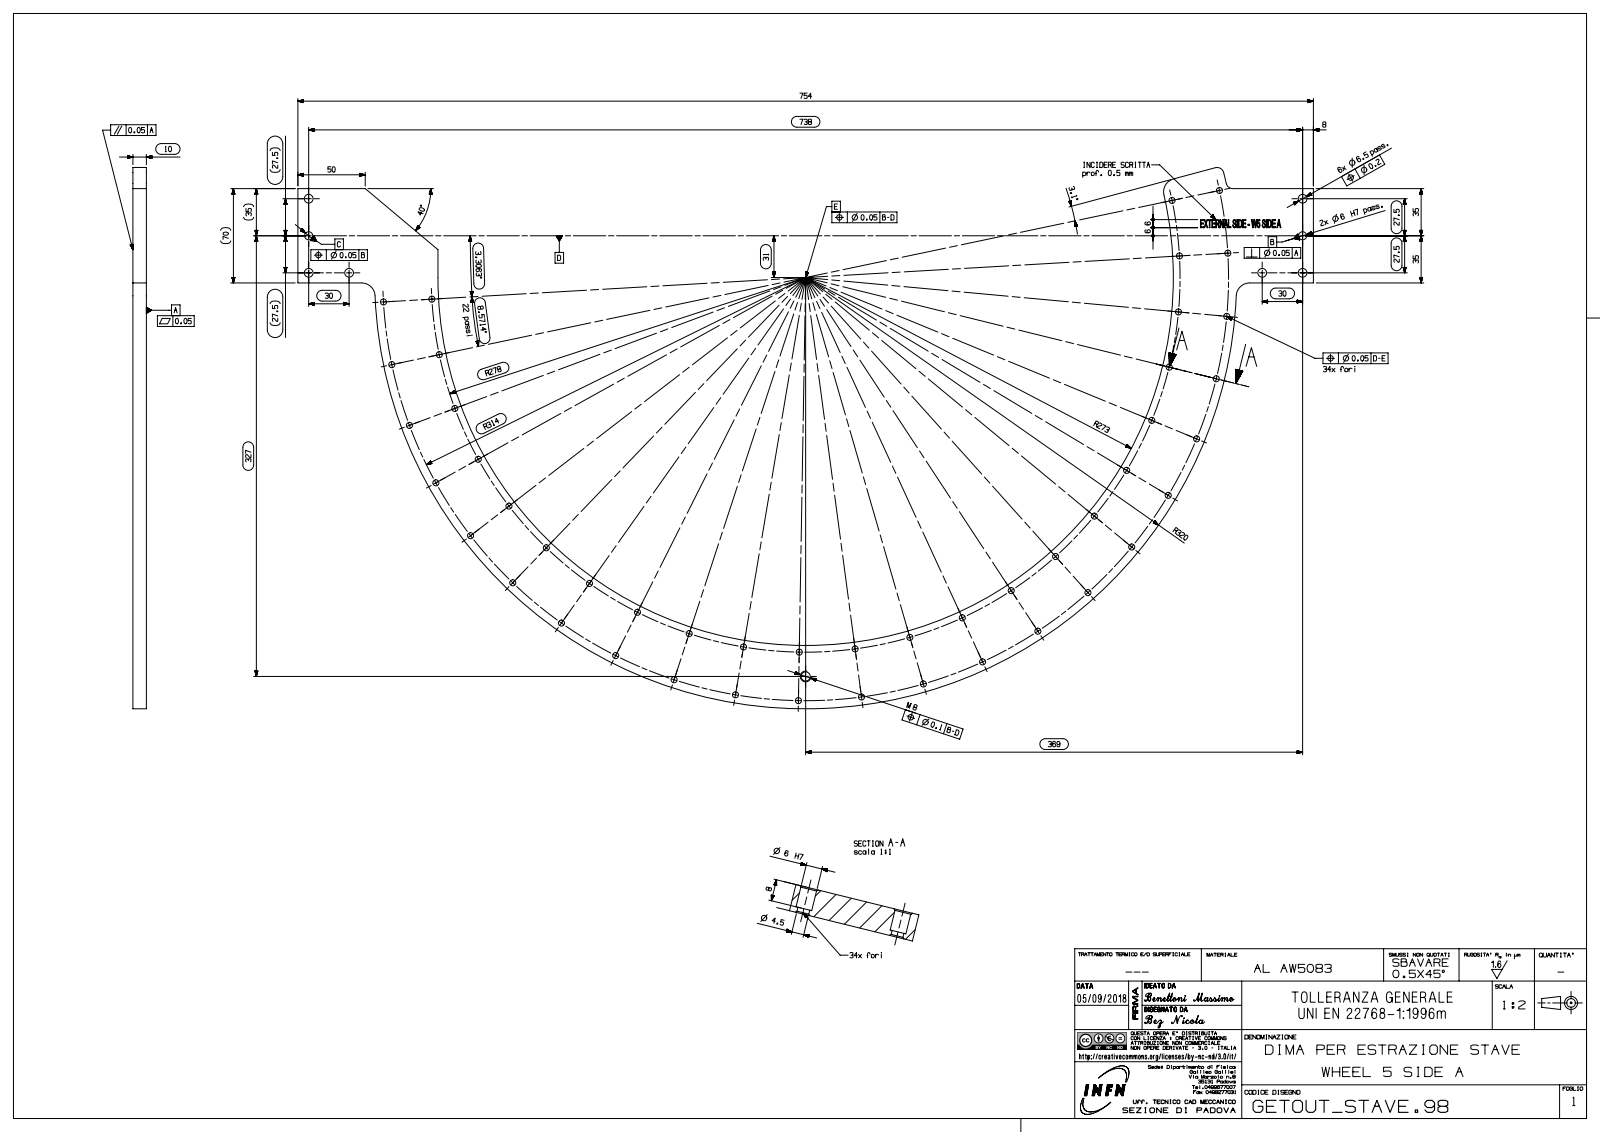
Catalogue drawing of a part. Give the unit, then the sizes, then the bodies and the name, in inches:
Units: inches
Overall size (bounding box): 29.685 × 15.815 × 0.394
Round holes (diameter × count): ⌀0.236 ×48, ⌀0.177 ×46, ⌀0.256 ×6, ⌀0.268 ×1
Partial cylindrical surfaces — rounded edges, fillets, slot ends (radius × count): R0.394 ×3, R0.197 ×2, R10.748 ×1, R12.598 ×1
Main face-to-face distances: 0.394, 2.756, 29.685, 0.315, 0.079, 25.591, 4.094, 0.374, 0.059, 0.02
Hole centre spacings: 5.367, 2.243, 3.746, 10.193, 1.848, 7.002, 8.617, 1.417
Volume: 34.14 in³ · Surface area: 227.8 in²
Bodies: 1 solid, 476 faces (223 planar, 109 cylindrical, 144 other)
Part name (STEP PRODUCT): bez8324385A6uyq
STEP written by: SIEMENS PLM Software NX 12.0 (AUTOMOTIVE_DESIGN)
